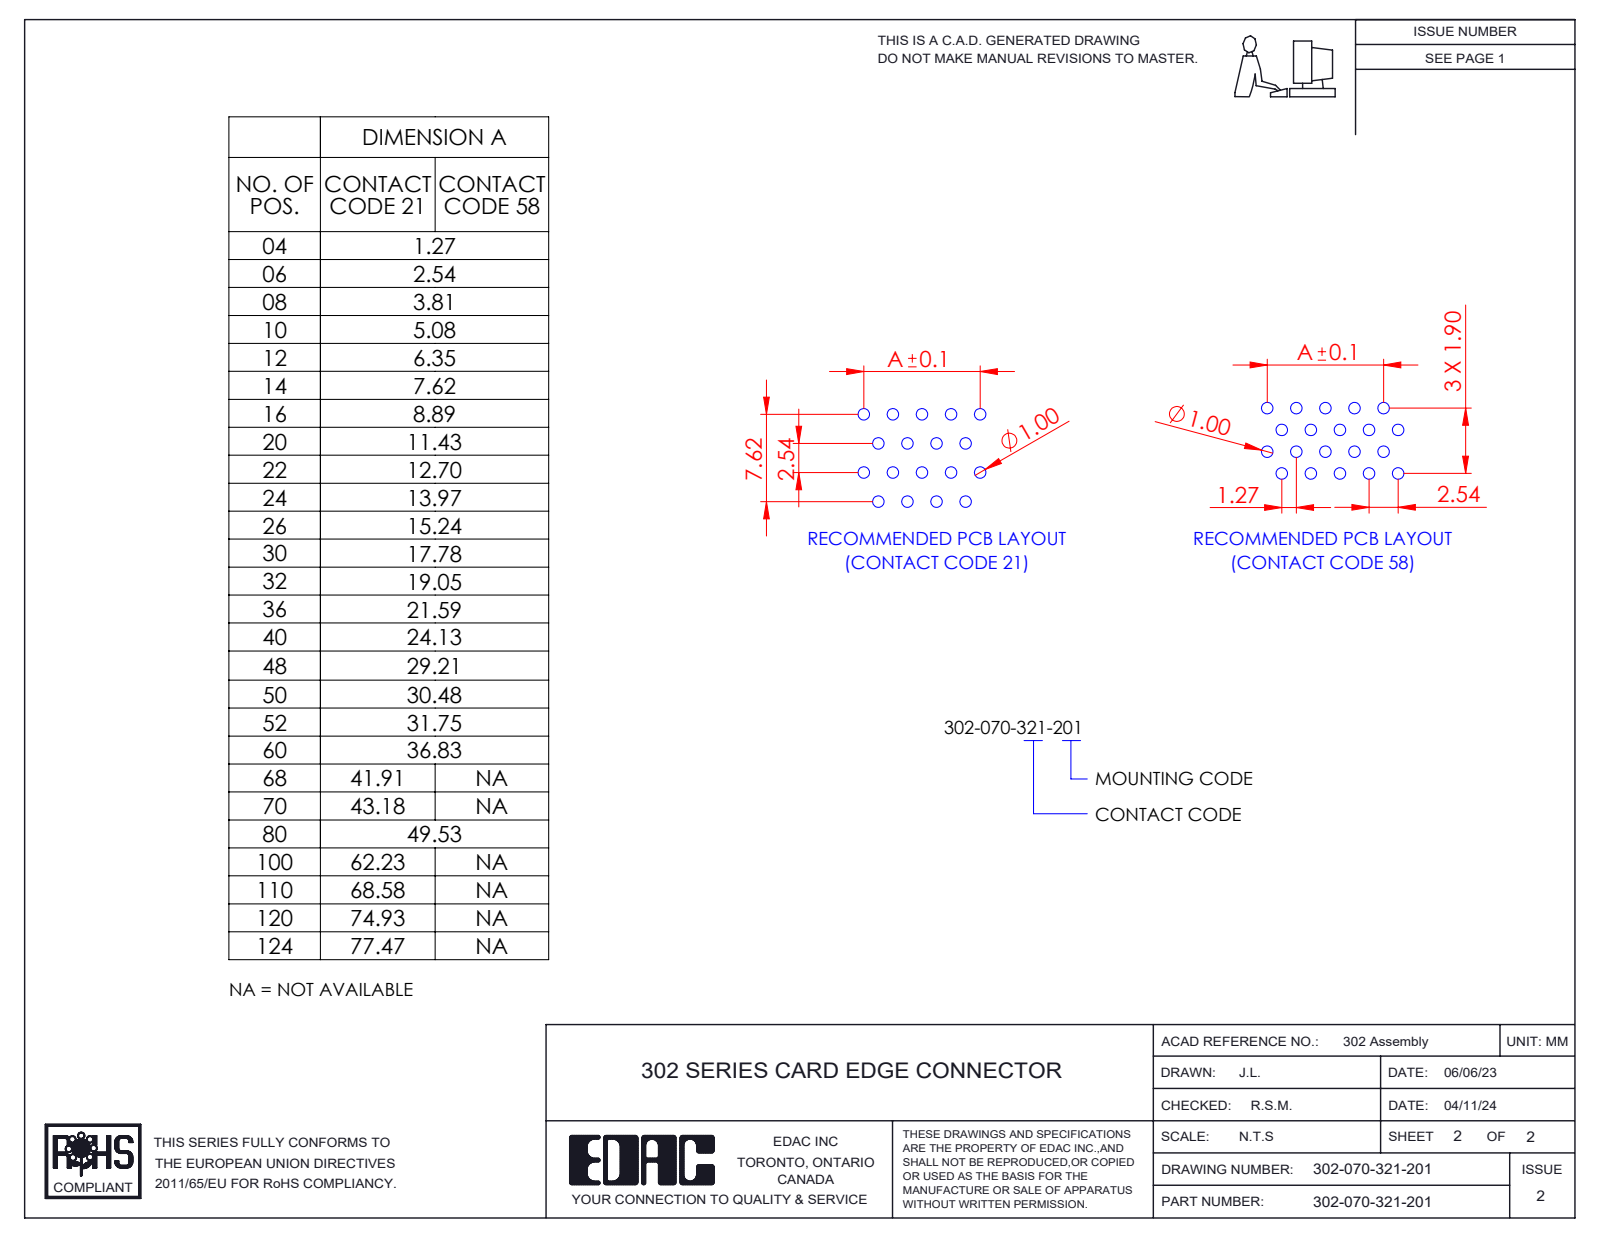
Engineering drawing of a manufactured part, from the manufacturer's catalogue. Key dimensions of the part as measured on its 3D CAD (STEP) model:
Part name (STEP PRODUCT): Contact_302-290-X21 (1); HSG_Vertical HSG; Contact_302-290-X21 (2); 302-070-321-201
STEP written by: SolidWorks 2023 (CONFIG_CONTROL_DESIGN)
Units: millimetres
Bodies: 71 solids, 3251 faces (2394 planar, 713 cylindrical, 144 other)
Overall size (bounding box): 50.55 × 17.63 × 8.88
Volume: 3 929 mm³ · Surface area: 10 748 mm²
Partial cylindrical surfaces — rounded edges, fillets, slot ends (radius × count): R0.2 ×78, R2.03 ×4, R2.09 ×4, R0.11 ×2, R0.4 ×2, R0.41 ×2, R1.25 ×2, R1.53 ×2
Main face-to-face distances: 2.54, 1.27, 5.08, 3.81, 7.62, 6.35, 8.88, 8.89, 10.16, 11.43
